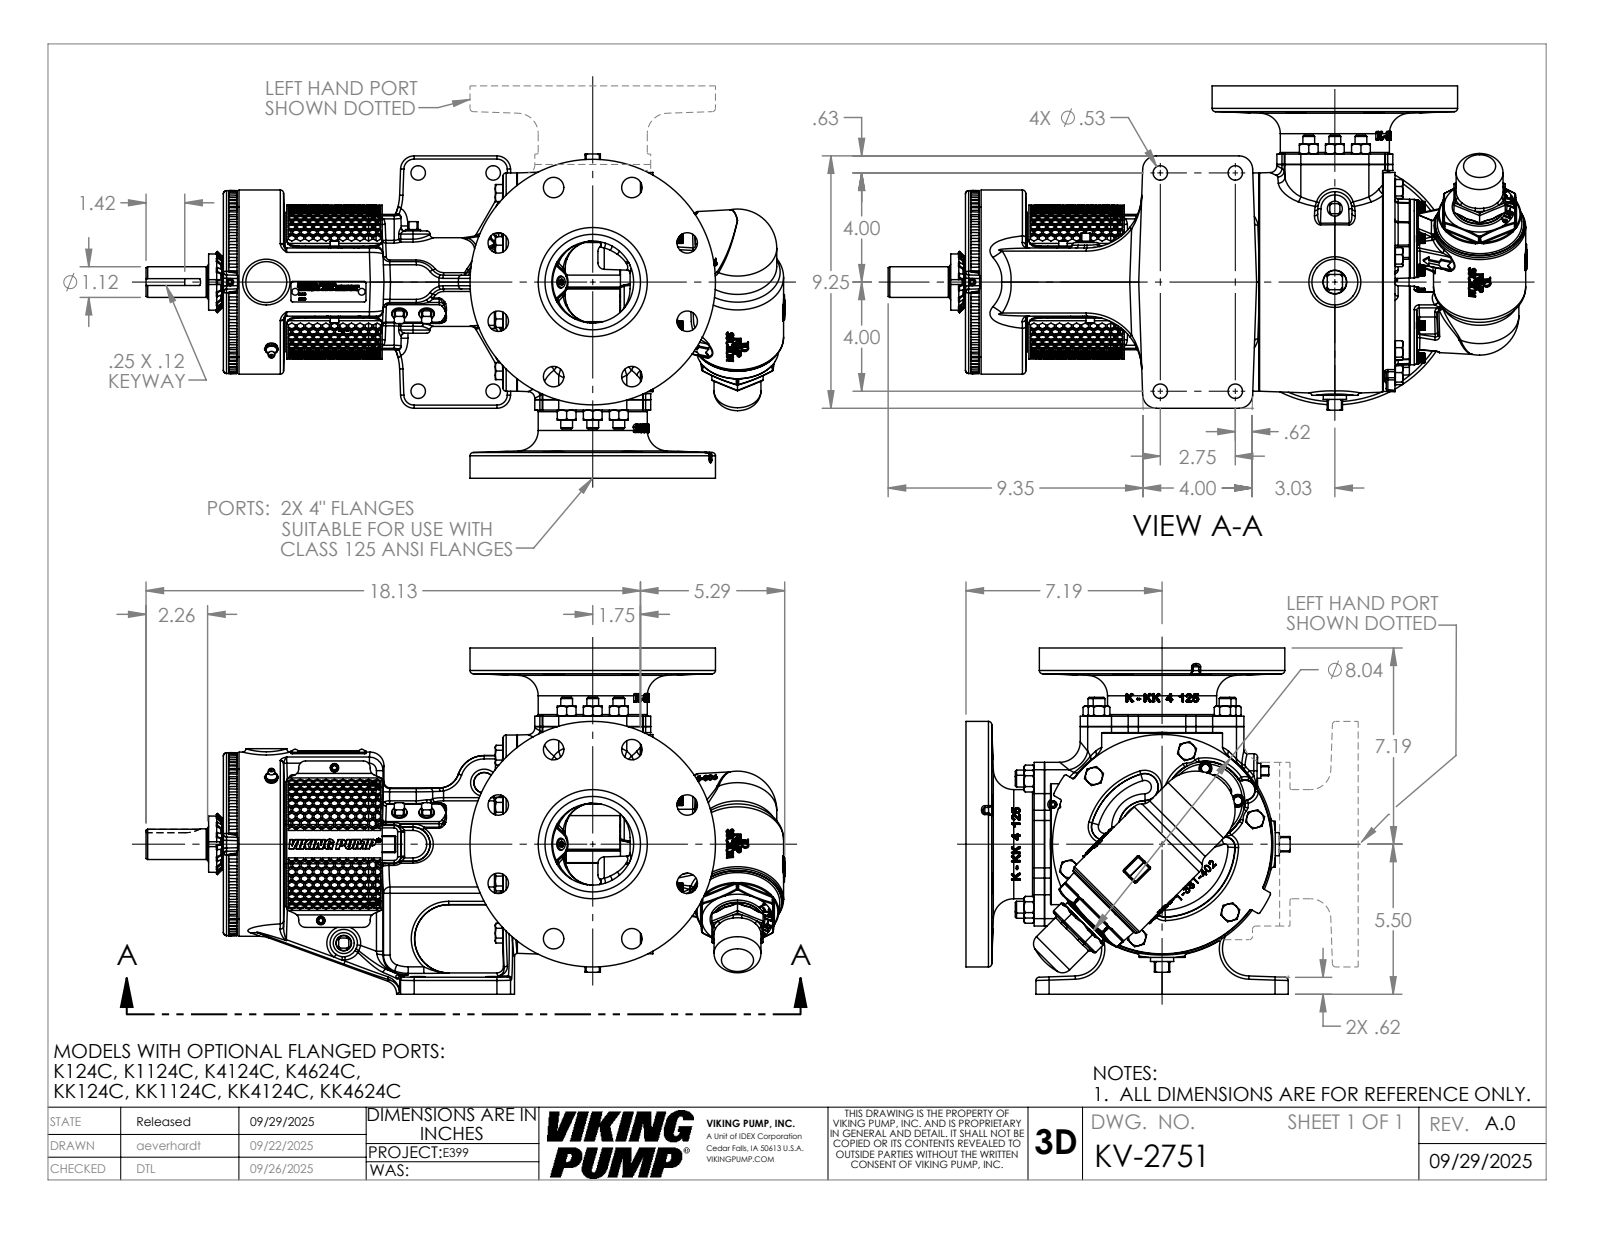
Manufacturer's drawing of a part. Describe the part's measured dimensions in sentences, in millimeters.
The part is named "KV-2751". Its 3-D file was written by "SolidWorks 2024 (AUTOMOTIVE_DESIGN)". It is 1 solid with 5357 faces: 1803 planar, 781 cylindrical and 2773 other. Overall it measures 594.8 by 322.3 by 301.9 millimeters. Its volume is 11 290 000 cubic millimeters and its surface area 885 800 square millimeters. Round holes: 16 of diameter 19.1, 8 of diameter 19.8, 6 of diameter 5, 6 of diameter 6.4, 4 of diameter 13.5, 2 of diameter 4, 2 of diameter 8, 2 of diameter 76.2, 2 of diameter 101.6, 1 of diameter 6.5, 1 of diameter 11.5, 1 of diameter 39.4. Round bosses or shafts: 12 of diameter 10.9, 11 of diameter 15.9, 8 of diameter 11.9, 3 of diameter 73.2, 3 of diameter 15.9, 3 of diameter 11.1, 3 of diameter 7.9, 2 of diameter 228.6. Partial cylindrical surfaces (rounded edges, fillets, slot ends): 80 of radius 3, 37 of radius 0.8, 18 of radius 6.1, 18 of radius 25.4, 16 of radius 3, 13 of radius 1.5, 10 of radius 6.4, 10 of radius 12.7. The main face-to-face distances are 322.3, 264.8, 63.5, 12.7, 135.2, 400, 73.4, 14.6, 120.7, 385.4. The hole center spacings are 72.9, 95.3, 134.7, 176, 76.2, 26.2, 126.8, 138.1.
